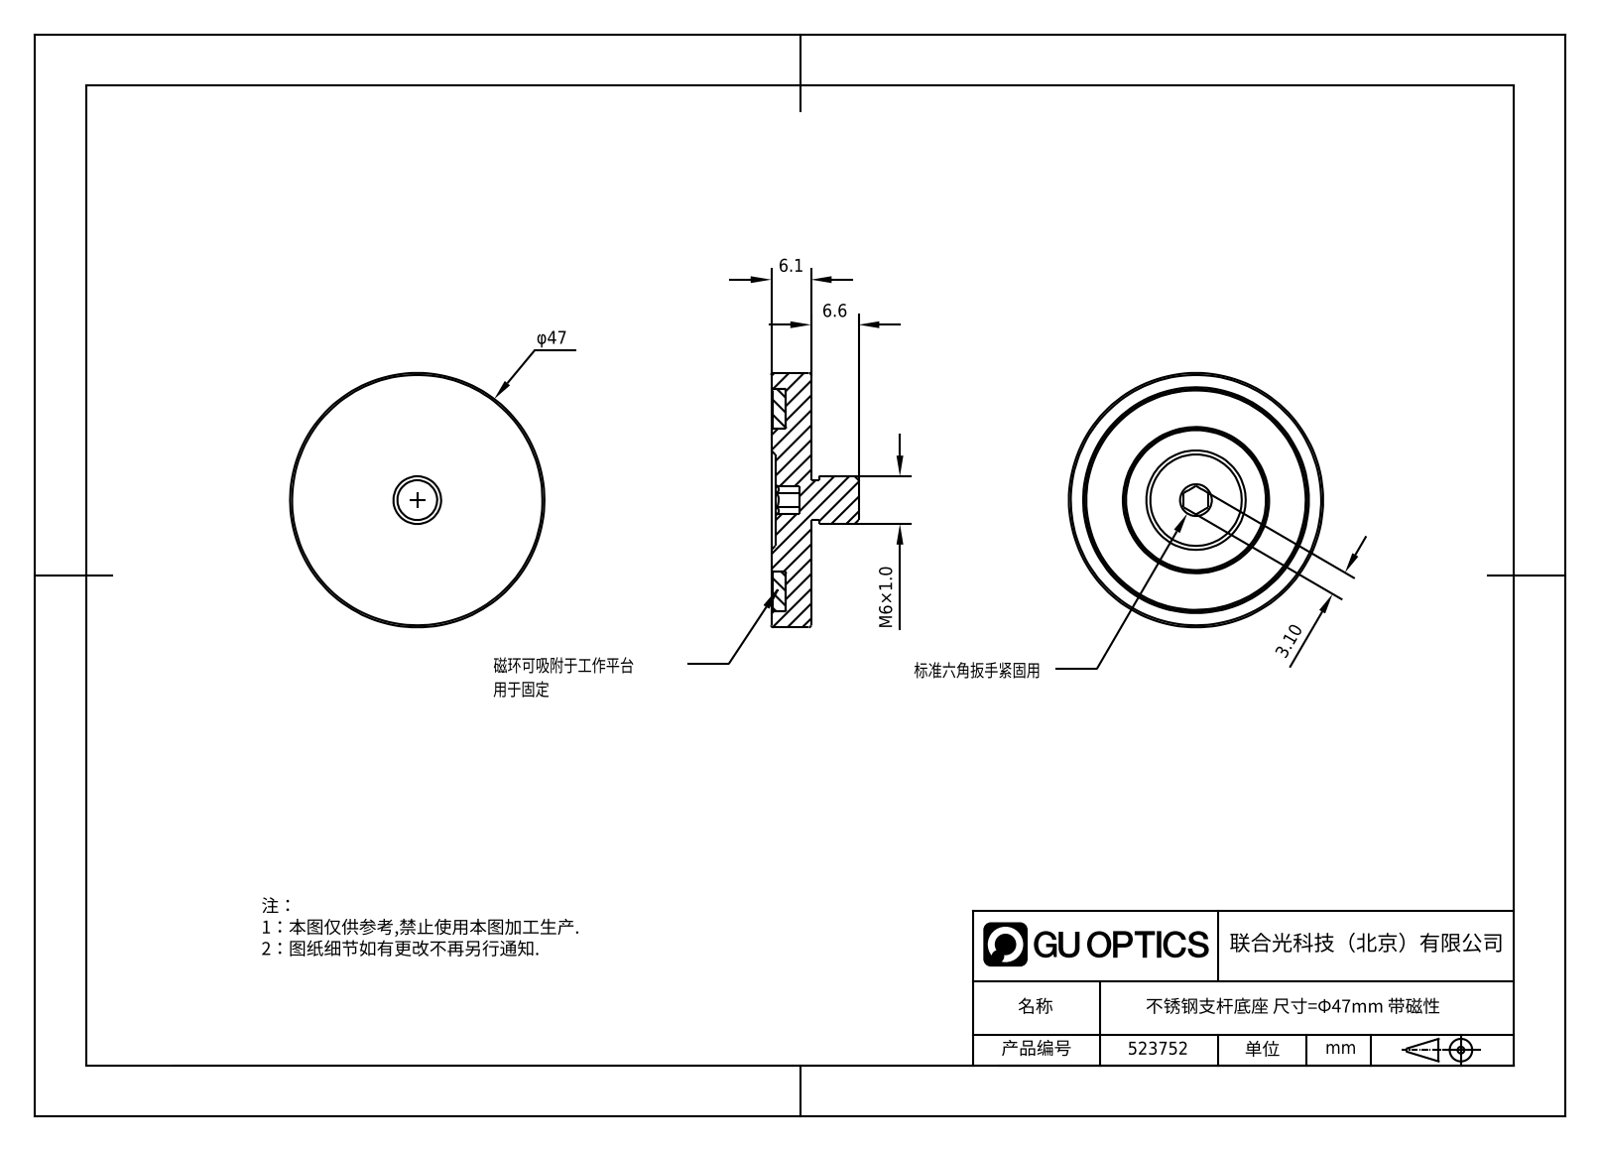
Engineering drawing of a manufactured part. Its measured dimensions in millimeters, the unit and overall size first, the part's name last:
Units: millimetres
Overall size (bounding box): 47 × 47 × 12.7
Round holes (diameter × count): ⌀28 ×1, ⌀40 ×1
Round bosses / shafts (diameter × count): ⌀47 ×1, ⌀6 ×1, ⌀5 ×1
Main face-to-face distances: 3.1, 2.8, 5.9, 3, 6.1, 5.6, 0.5, 2.5, 6.6, 12.7
Volume: 10 366 mm³ · Surface area: 6 990 mm²
Bodies: 2 solids, 32 faces (16 planar, 7 cylindrical, 9 other)
Part name (STEP PRODUCT): 523752
STEP written by: SolidWorks 2020 (CONFIG_CONTROL_DESIGN)
